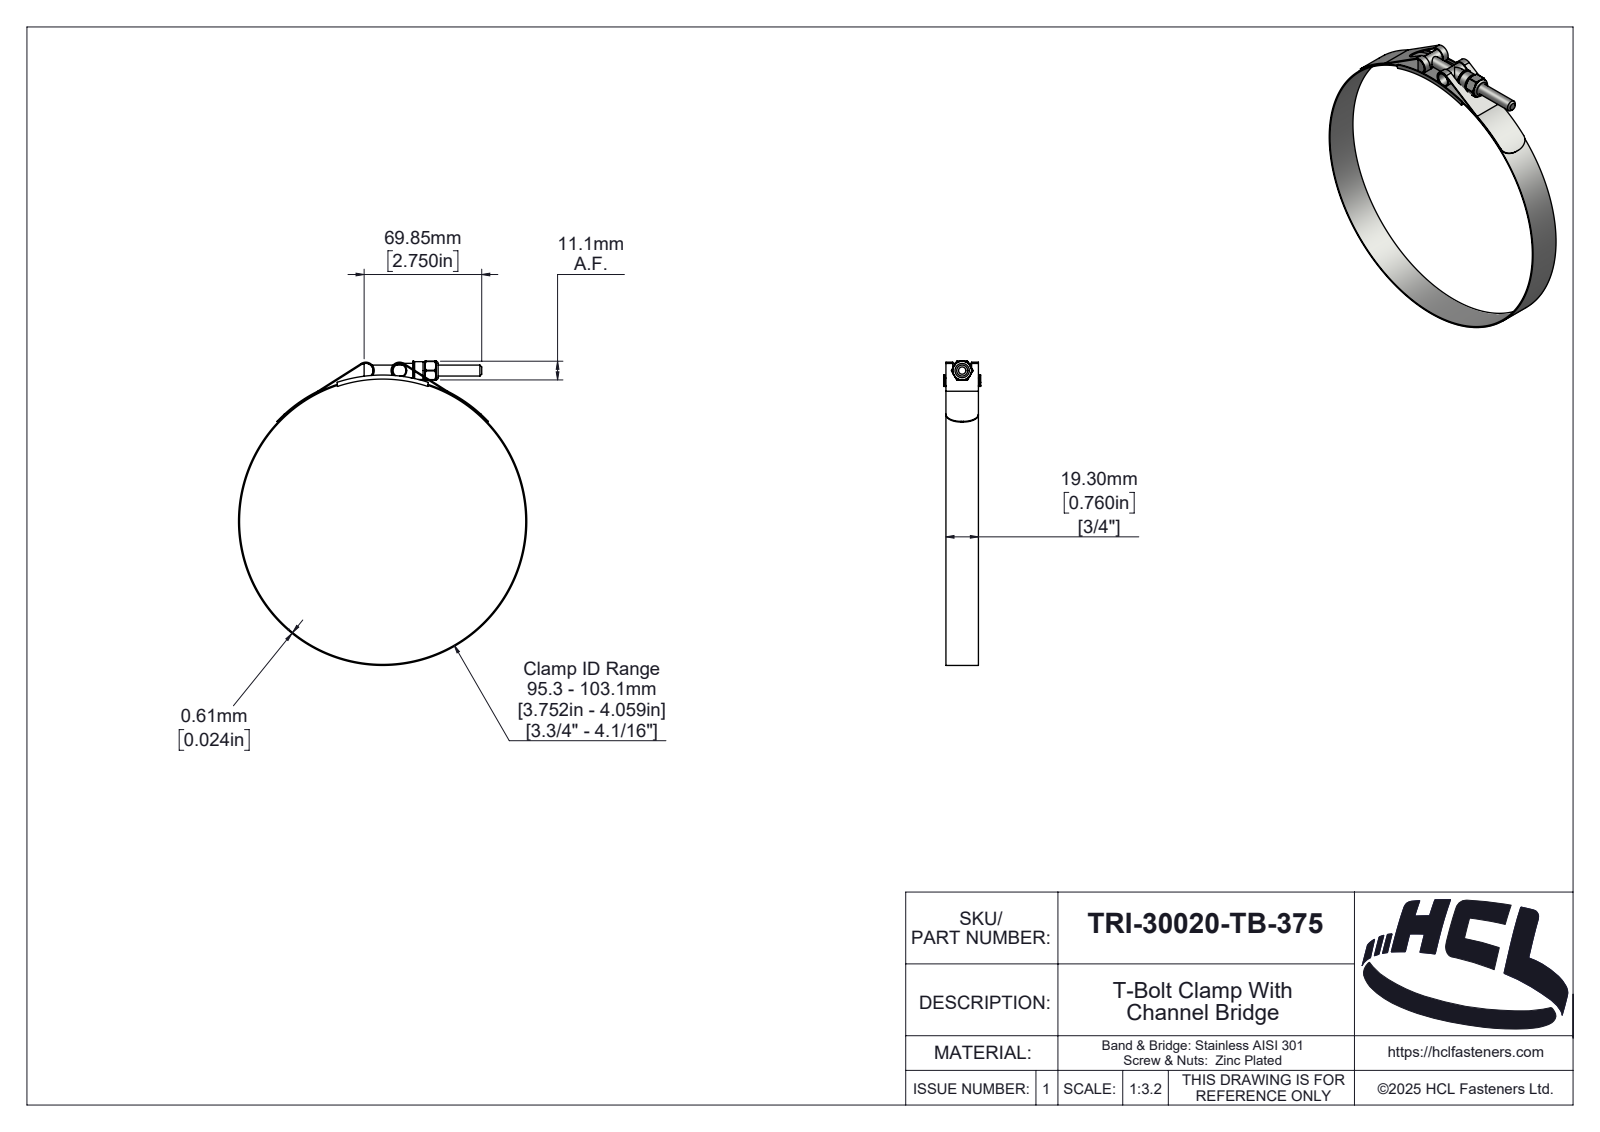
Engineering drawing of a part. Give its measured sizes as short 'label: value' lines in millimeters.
name: TRI-30020-TB-375
written by: SolidWorks 2025 (AUTOMOTIVE_DESIGN)
unit: mm
bodies: 6 solids, 330 faces (44 planar, 122 cylindrical, 164 other)
size: 180.77 × 171.22 × 22
volume: 12 542 mm³; area: 32 761 mm²
holes: 1× ⌀5.4, 1× ⌀6.35, 1× ⌀6.5, 1× ⌀7.58, 1× ⌀170
bosses: 2× ⌀8.58, 1× ⌀171.22, 1× ⌀10.58
rounds: 6× R0.39, 2× R0.5, 2× R4.39, 2× R5, 1× R0.59, 1× R2.42, 1× R3.03, 1× R3.19
face distances: 0.61, 19.3, 1.35, 20.65, 0.74, 21.39, 20.04, 22, 11.11, 20.78
hole spacings: 90
